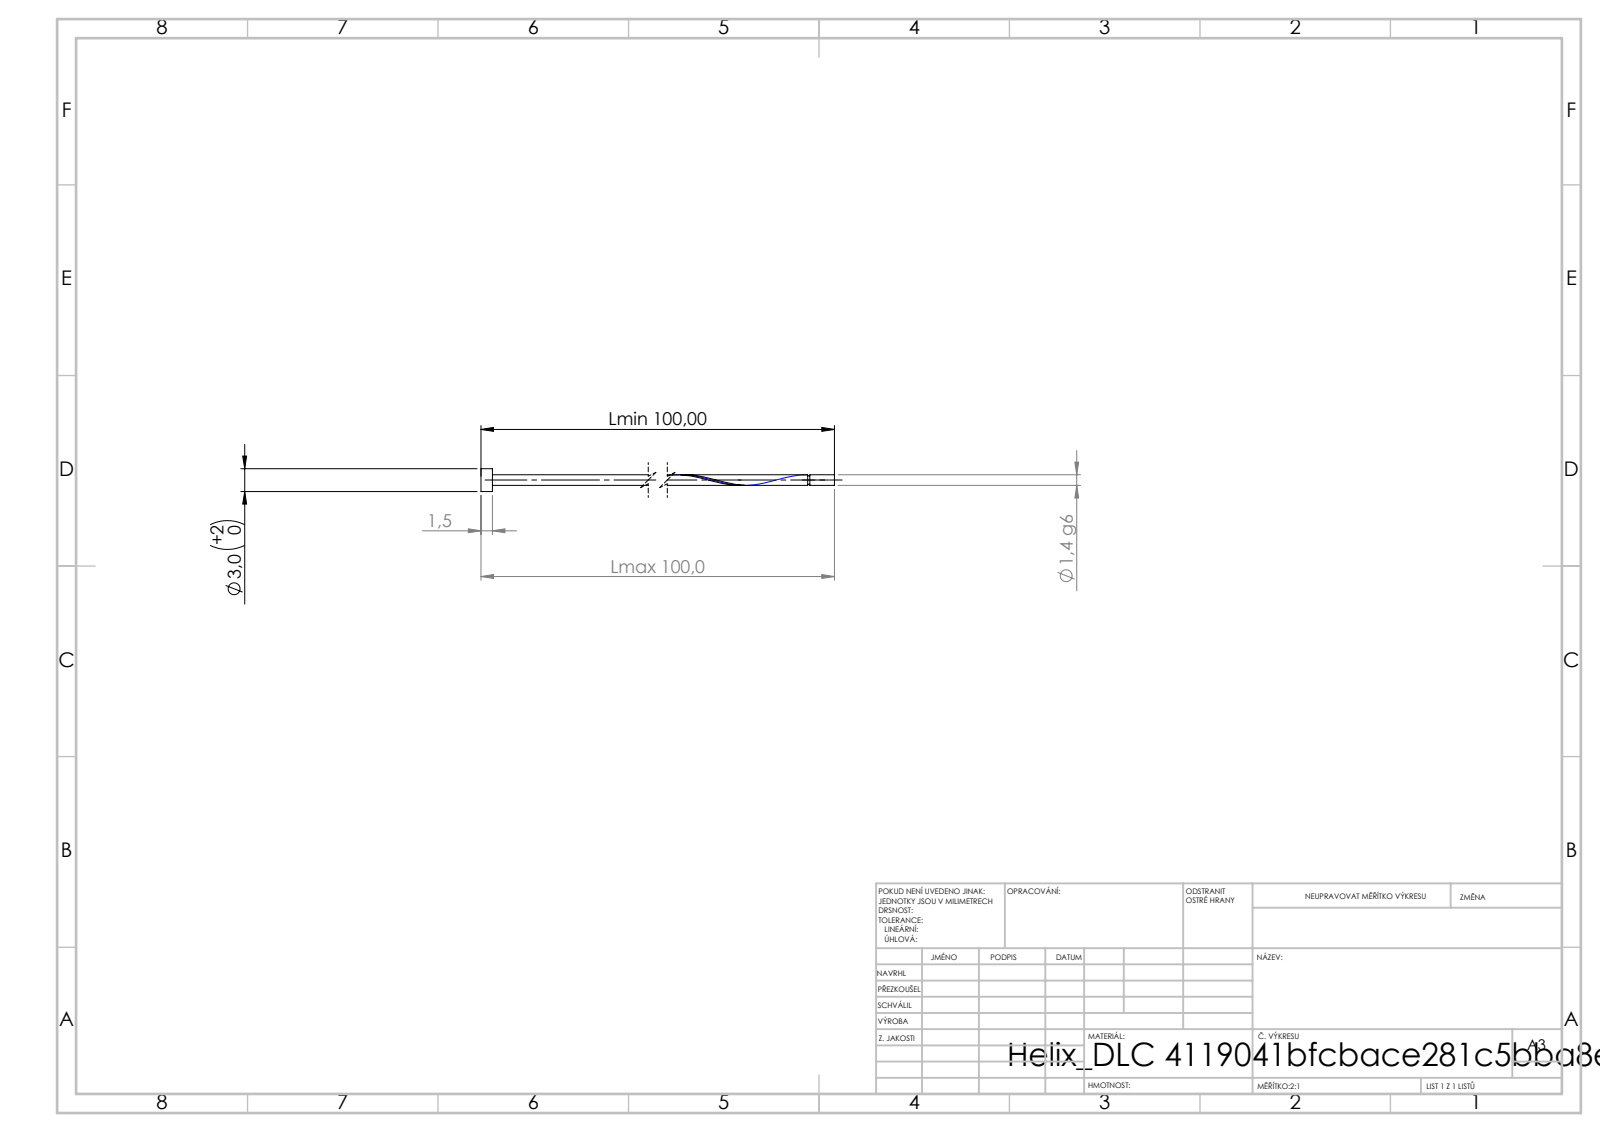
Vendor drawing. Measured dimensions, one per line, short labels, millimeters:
written by: SolidWorks 2019 (CONFIG_CONTROL_DESIGN)
unit: mm
bodies: 1 solid, 16 faces (6 planar, 9 cylindrical, 1 other)
size: 100 × 3 × 3
volume: 195 mm³; area: 616 mm²
bosses: 1× ⌀3, 1× ⌀1.4, 1× ⌀1.12
face distances: 1.5, 100, 98.5, 96.76, 95.26, 3.24, 96.48, 94.98, 3.52, 46.48
